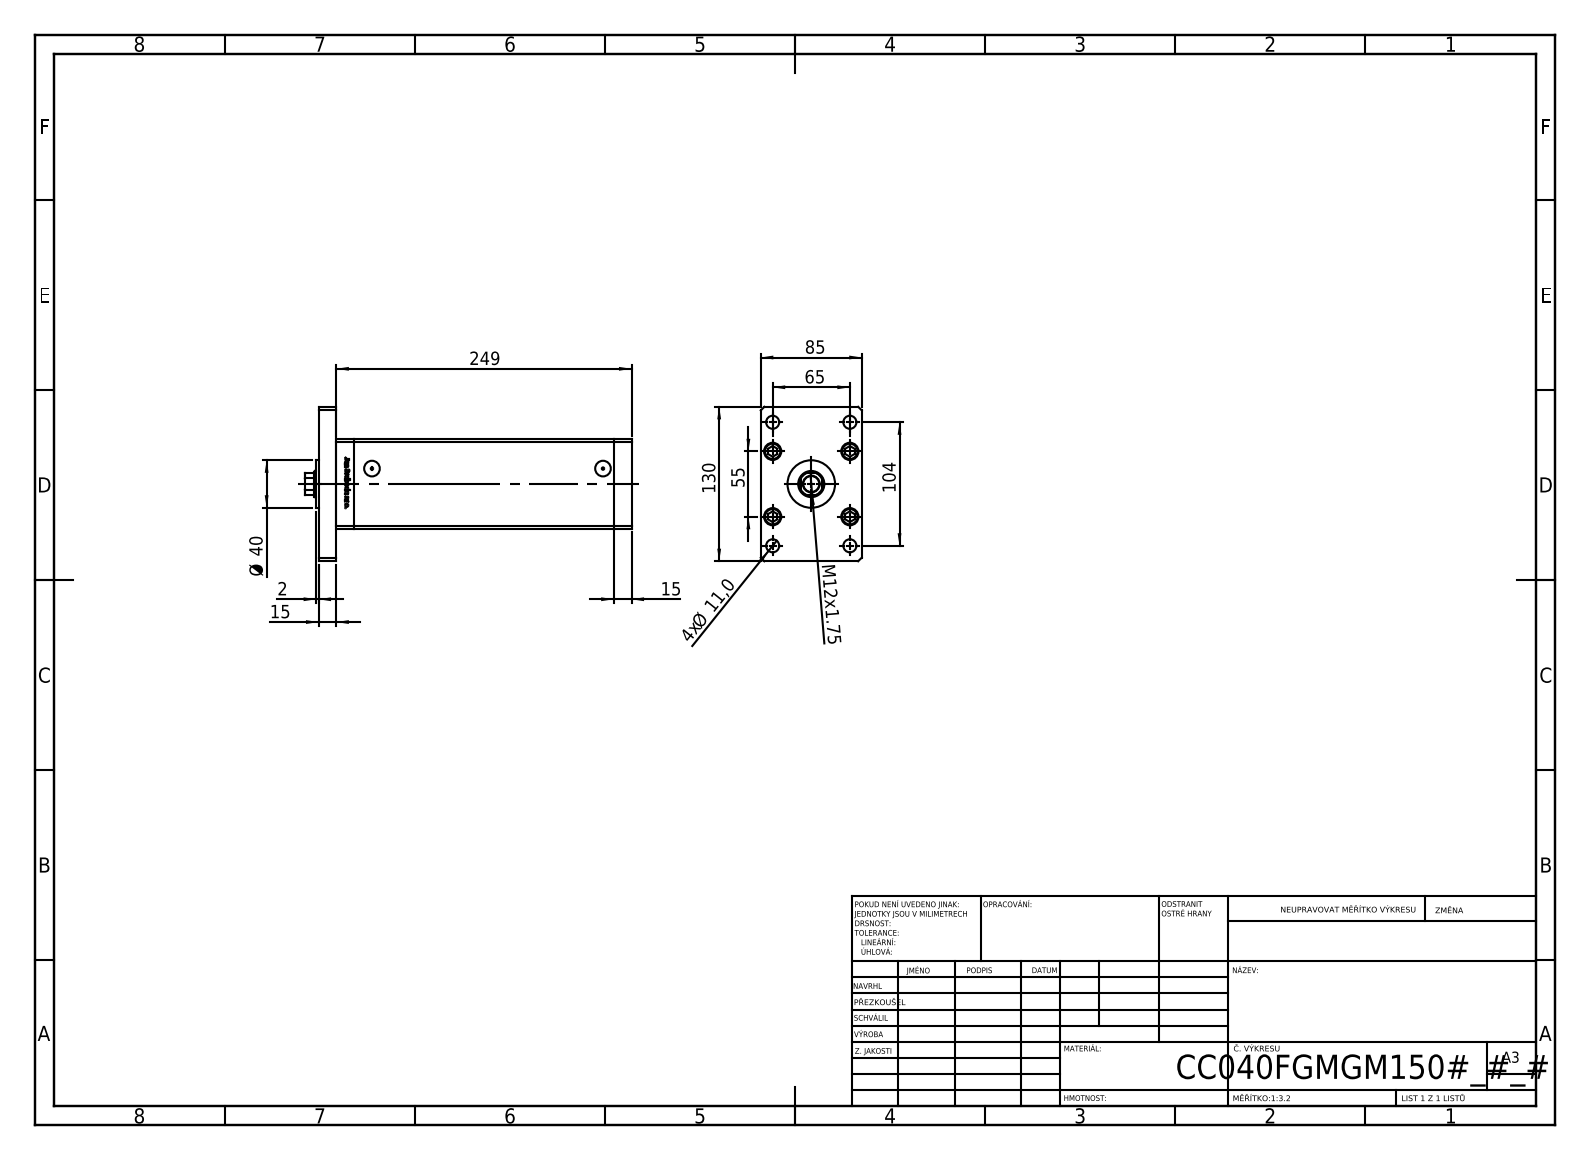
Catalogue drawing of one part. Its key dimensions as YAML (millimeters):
part_name: "V220C BACK_F; V220C_VC_F; V220C_F_MIDDLE; V220C_FRONT_F (+2 more)"
step_written_by: "SolidWorks 2019 (CONFIG_CONTROL_DESIGN)"
units: millimeters
bodies: {solids: 19, faces: 1308, planar: 515, cylindrical: 187, other: 606}
overall_size: [275, 130, 85]
volume: 1536000
surface_area: 236256
round_holes:
  - {diameter: 11, count: 9}
  - {diameter: 15.5, count: 5}
  - {diameter: 10, count: 4}
  - {diameter: 14.5, count: 4}
  - {diameter: 2, count: 2}
  - {diameter: 13.16, count: 2}
  - {diameter: 13.5, count: 1}
  - {diameter: 22, count: 1}
  - {diameter: 23.5, count: 1}
round_bosses_or_shafts:
  - {diameter: 8, count: 9}
  - {diameter: 14.5, count: 5}
  - {diameter: 40, count: 1}
partial_cylinders:
  - {radius: 0.93, count: 2}
  - {radius: 10.5, count: 1}
face_to_face_distances: [15, 85, 75, 233.5, 248.5, 218.5, 30, 263.5, 10.5, 27.5]
hole_center_spacings: [28, 24.5, 42.57, 61.32, 65, 69.46, 79.5, 102.69]
